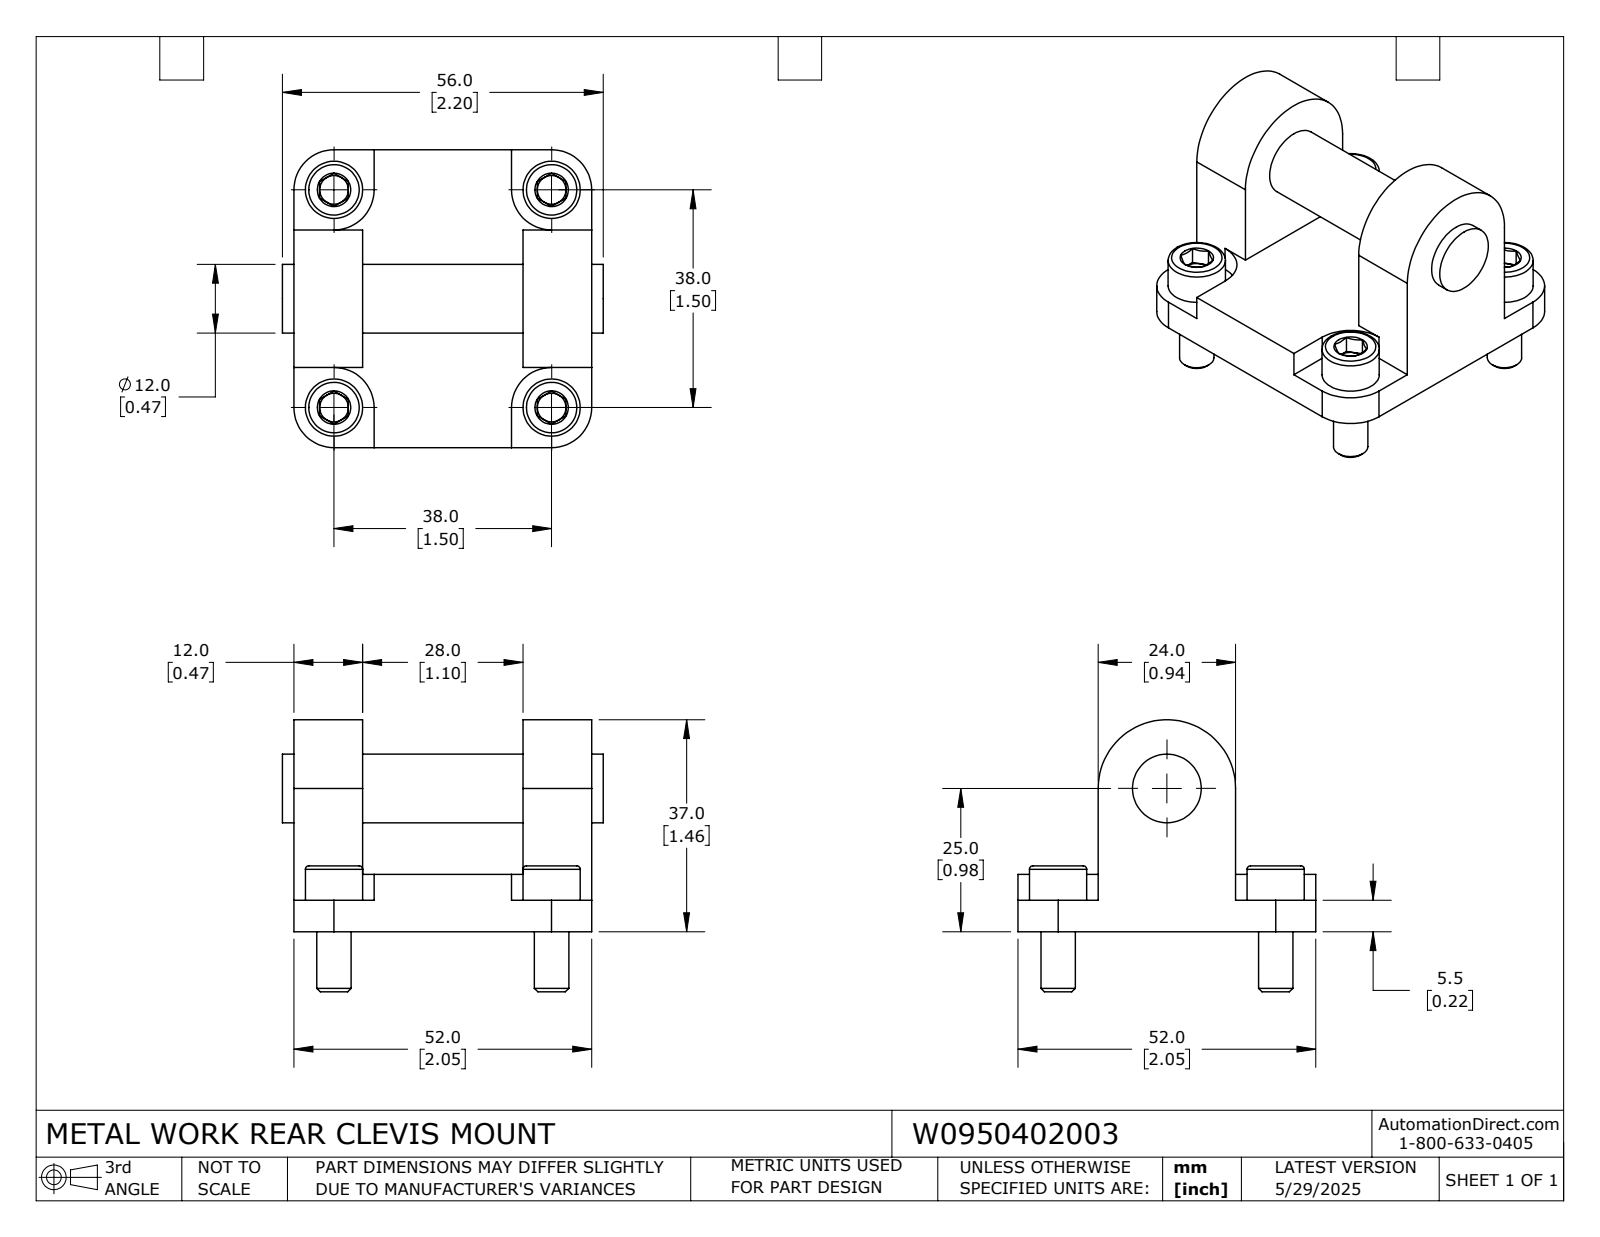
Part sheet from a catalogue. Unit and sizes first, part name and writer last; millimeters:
Units: millimetres
Overall size (bounding box): 56 × 52 × 47.5
Round holes (diameter × count): ⌀6.6 ×4, ⌀35 ×1
Round bosses / shafts (diameter × count): ⌀10 ×4, ⌀6 ×4, ⌀12 ×1
Partial cylindrical surfaces — rounded edges, fillets, slot ends (radius × count): R7 ×4, R12 ×1
Main face-to-face distances: 10, 52, 40, 14, 3, 7, 12, 4.5, 1.5, 38
Hole centre spacings: 26.9, 38, 53.7
Volume: 37 050 mm³ · Surface area: 15 330 mm²
Bodies: 5 solids, 181 faces (83 planar, 42 cylindrical, 56 other)
Part name (STEP PRODUCT): W0950402003
STEP written by: SolidWorks 2024 (CONFIG_CONTROL_DESIGN)
